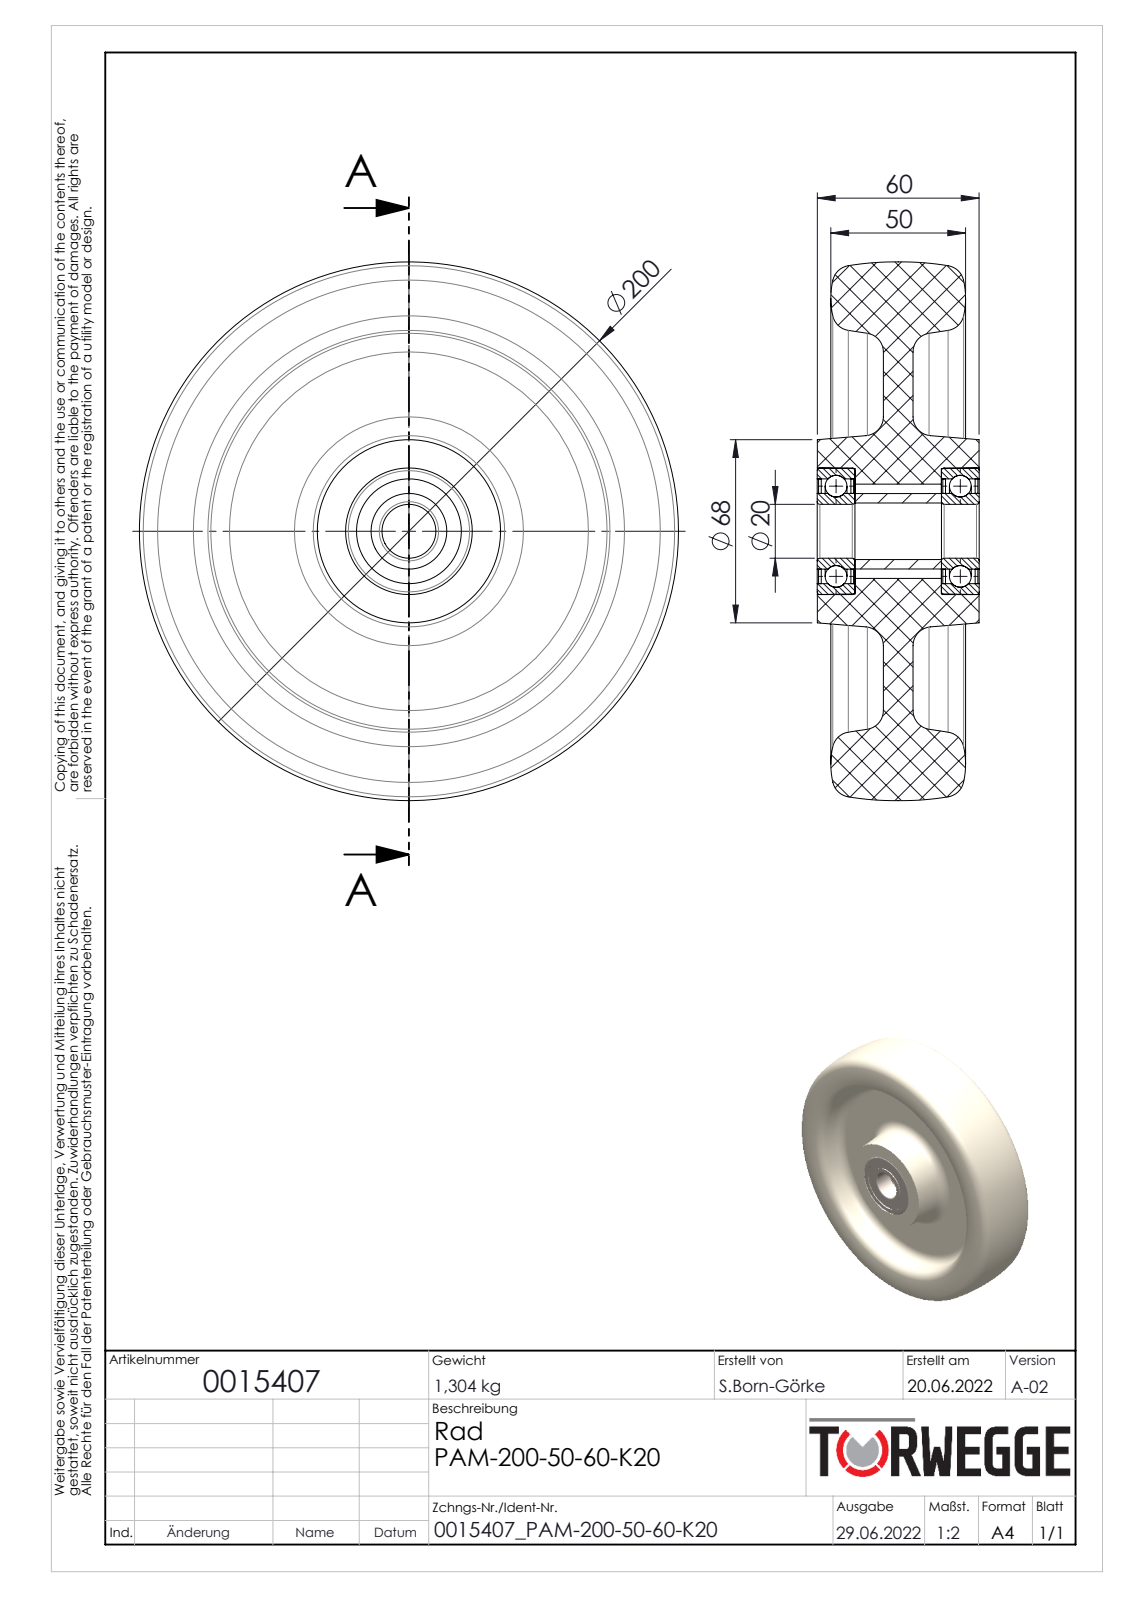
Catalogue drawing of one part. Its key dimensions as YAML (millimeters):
part_name: "0015407"
step_written_by: "SolidWorks 2020 (AUTOMOTIVE_DESIGN)"
units: millimeters
bodies: {solids: 12, faces: 142, planar: 24, cylindrical: 46, other: 72}
overall_size: [200.02, 200, 60.1]
volume: 1012000
surface_area: 145159
round_holes:
  - {diameter: 20, count: 1}
  - {diameter: 21, count: 1}
  - {diameter: 28.1, count: 1}
  - {diameter: 35, count: 1}
  - {diameter: 38.9, count: 1}
round_bosses_or_shafts:
  - {diameter: 47, count: 1}
  - {diameter: 28, count: 1}
face_to_face_distances: [11, 24.5, 35.5, 46.1, 46.05, 14, 0.5, 1.5, 12.5, 13.5]
